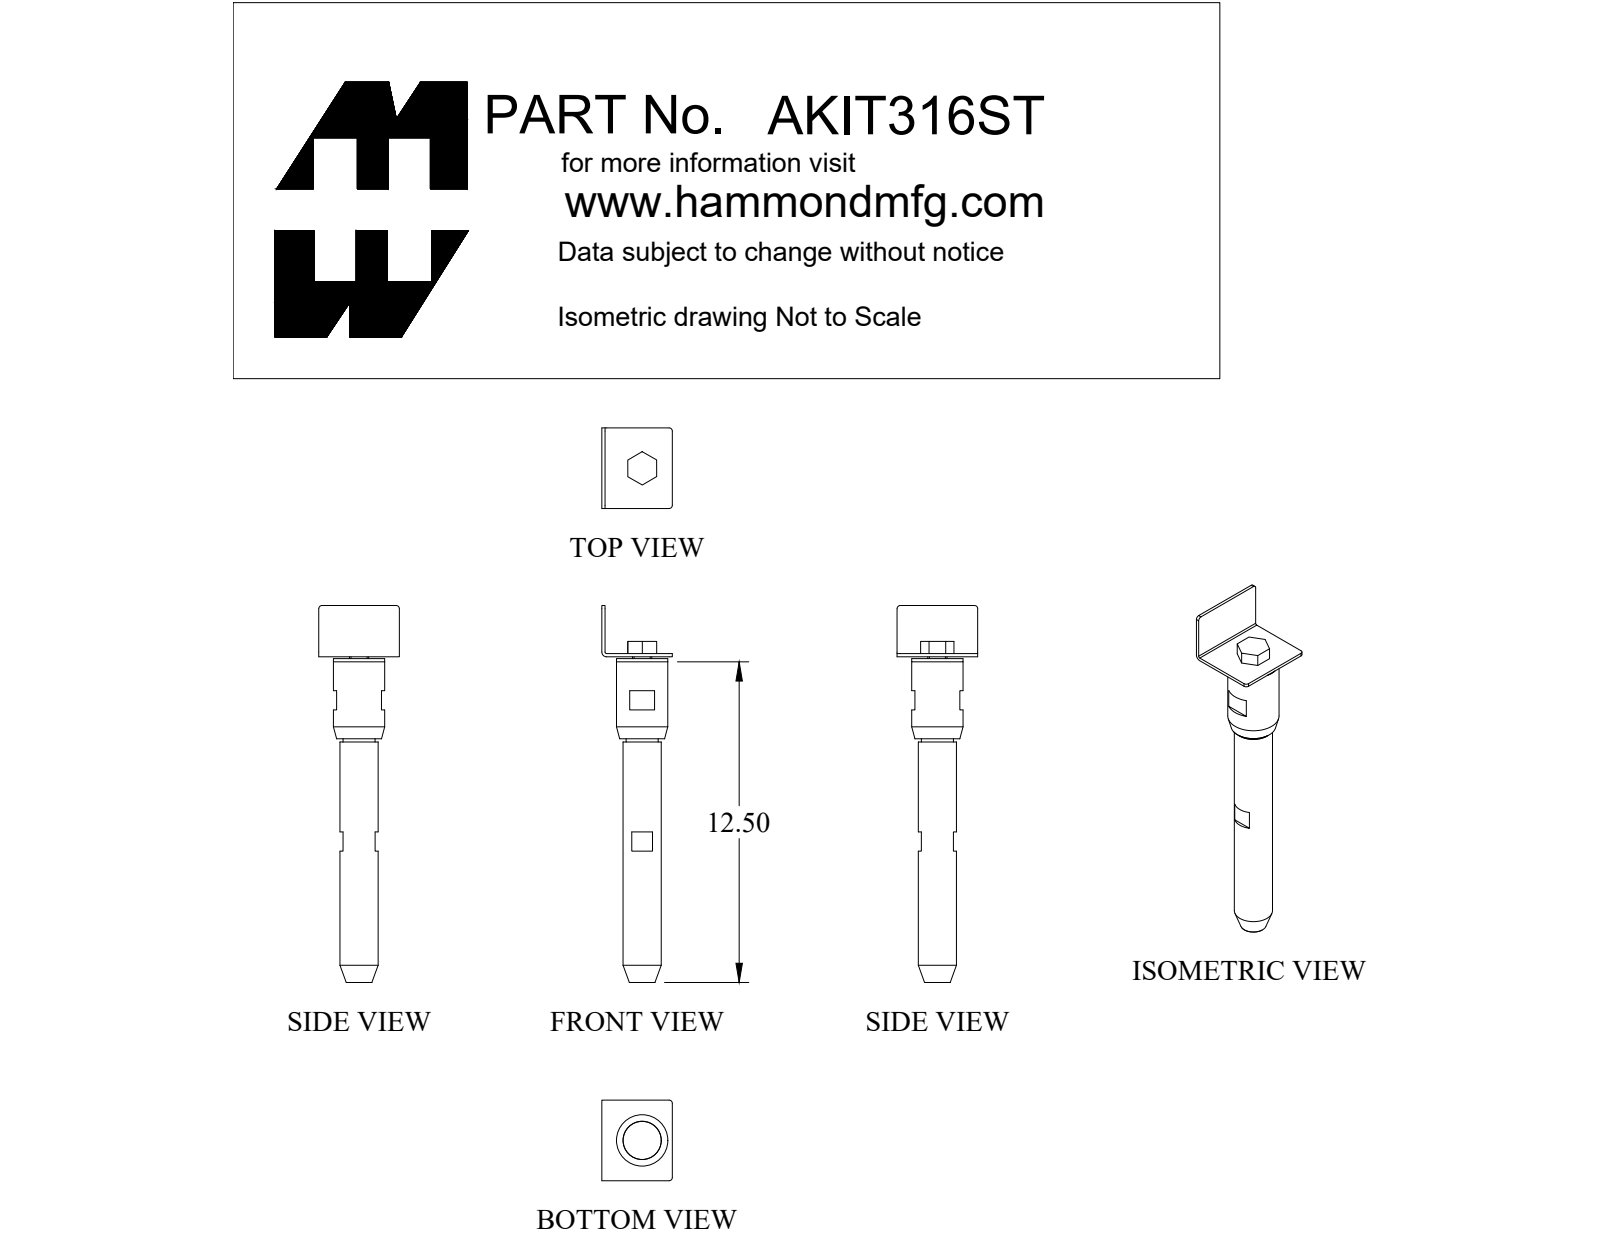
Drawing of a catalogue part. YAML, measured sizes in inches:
part_name: "AKIT316ST"
step_written_by: "SolidWorks 2019 (CONFIG_CONTROL_DESIGN)"
units: inches
bodies: {solids: 6, faces: 79, planar: 40, cylindrical: 20, other: 19}
overall_size: [14.697, 3.144, 2.75]
volume: 25.99
surface_area: 146.2
round_holes:
  - {diameter: 0.719, count: 1}
  - {diameter: 0.75, count: 1}
  - {diameter: 0.875, count: 1}
  - {diameter: 1.35, count: 1}
  - {diameter: 1.493, count: 1}
round_bosses_or_shafts:
  - {diameter: 2, count: 1}
  - {diameter: 1.489, count: 1}
  - {diameter: 1.327, count: 1}
  - {diameter: 1.249, count: 1}
partial_cylinders:
  - {radius: 0.125, count: 4}
  - {radius: 0.06, count: 1}
  - {radius: 0.185, count: 1}
face_to_face_distances: [0.125, 0.322, 0.197, 0.125, 0.072, 0.197, 0.697, 1.5, 3.322, 0.625]
